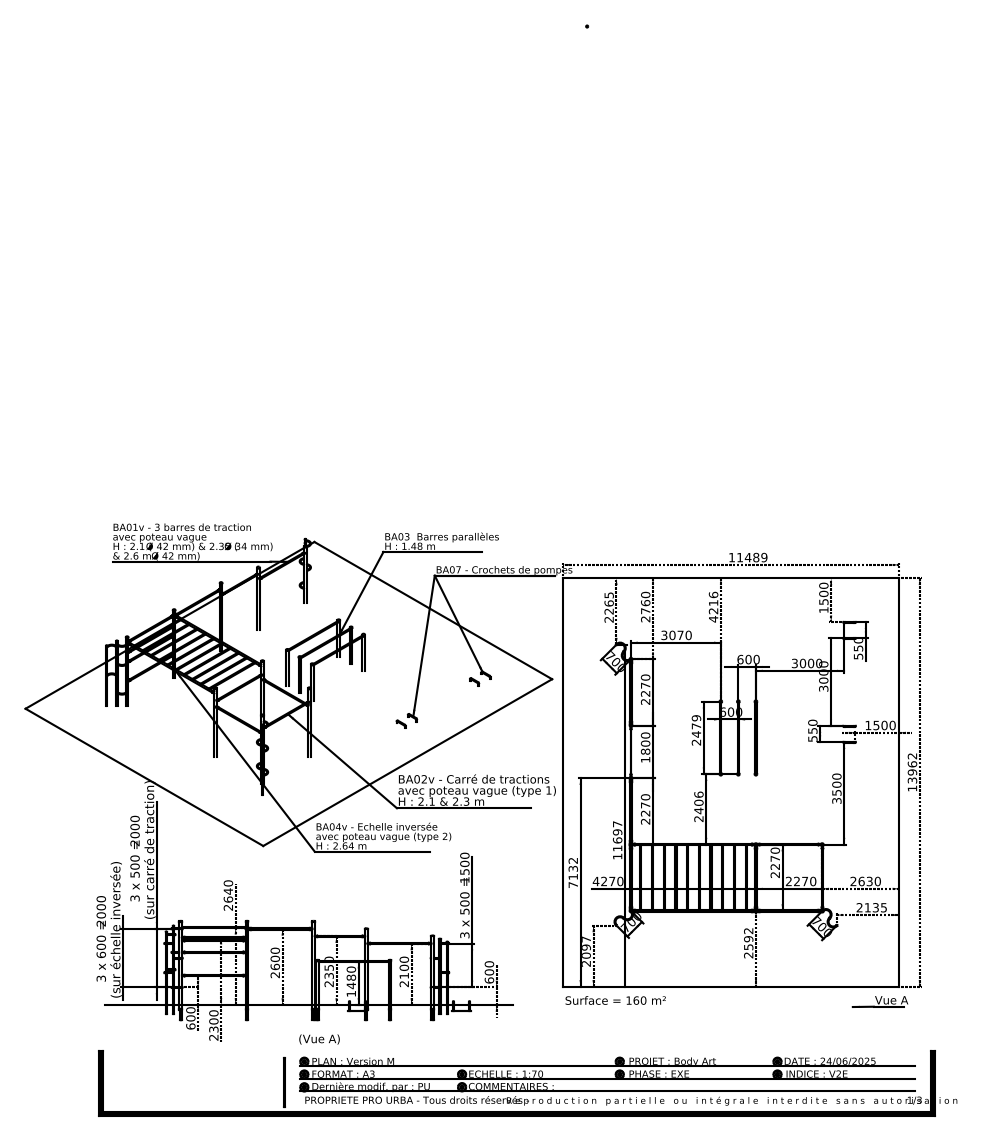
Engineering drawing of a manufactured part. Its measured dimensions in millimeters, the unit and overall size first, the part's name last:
Units: millimetres
Overall size (bounding box): 13962 × 11489 × 3375
Round holes (diameter × count): ⌀6.65 ×40, ⌀8 ×40, ⌀8.75 ×40, ⌀9 ×40, ⌀15 ×40, ⌀43.4 ×23, ⌀36 ×16, ⌀84.9 ×15, ⌀37.2 ×13, ⌀29.7 ×12, ⌀20 ×10, ⌀79.9 ×9
Round bosses / shafts (diameter × count): ⌀13 ×40, ⌀42.4 ×29, ⌀88.9 ×15, ⌀33.7 ×13, ⌀35 ×10, ⌀60.3 ×2, ⌀52.1 ×2, ⌀27 ×1
Main face-to-face distances: 60, 150, 95, 2100.2, 200, 2640.2, 35, 500, 540, 2125
Hole centre spacings: 2270, 130.08, 38, 71, 109, 400, 4270, 800
Bodies: 220 solids, 4294 faces (1386 planar, 1532 cylindrical, 1376 other)
Part name (STEP PRODUCT): Traverse + visserie_Diam. 42.4; Traverses_Diam. 42.4<Brut d''''usinage>; Traverse + visserie_Assemblage echelle inversée; Poteau_Poteau double 180° - 2100 & 2350 avec diam33.7 sur h2300 (+8 more)
STEP written by: SolidWorks 2025 (AUTOMOTIVE_DESIGN)
